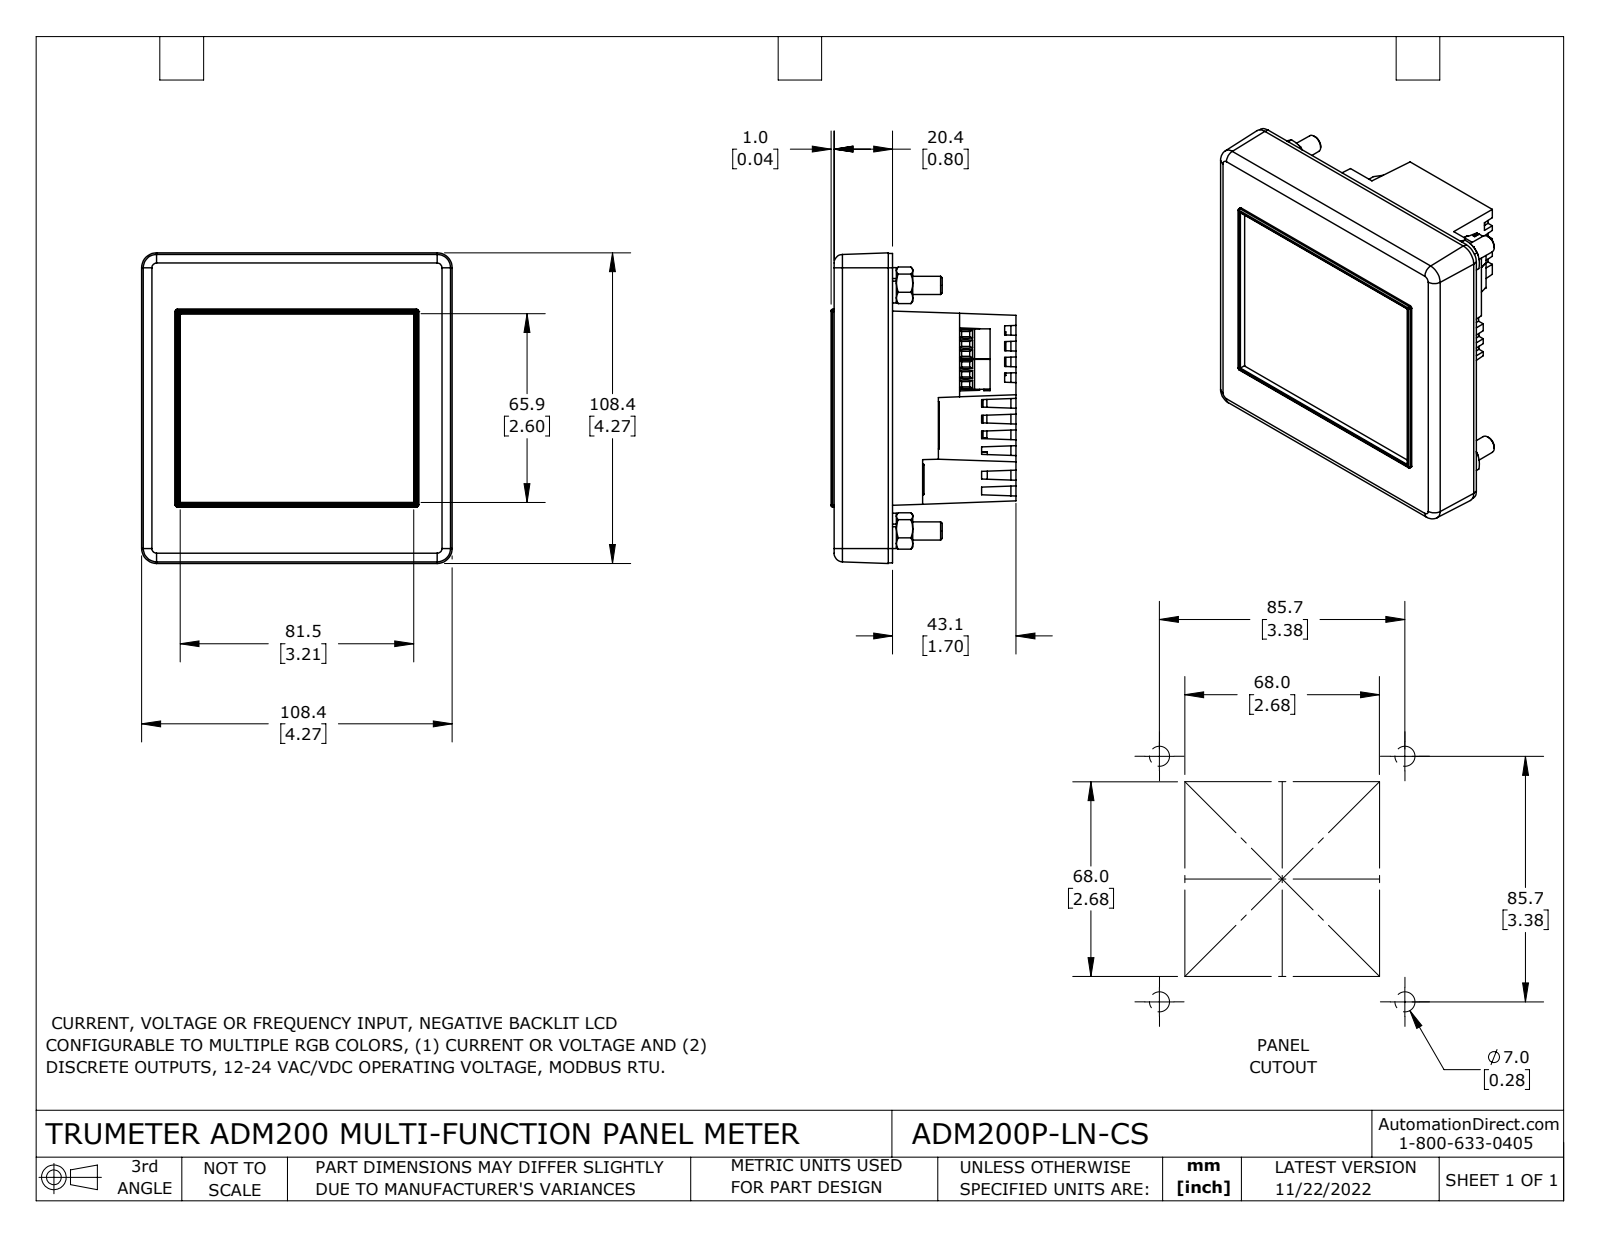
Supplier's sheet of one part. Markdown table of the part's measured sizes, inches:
| quantity | value |
| --- | --- |
| part name | ADM200P-LN-CS |
| STEP written by | SolidWorks 2021 (CONFIG_CONTROL_DESIGN) |
| units | inches |
| bodies | 23 solids, 2059 faces (1384 planar, 290 cylindrical, 385 other) |
| overall size | 4.269 × 4.269 × 2.541 |
| volume | 7.808 in³ |
| surface area | 190.8 in² |
| round holes (diameter × count) | 0.071 × 9, 0.114 × 6, 0.118 × 5, 0.213 × 4, 0.25 × 4, 0.26 × 4, 0.295 × 4, 0.154 × 2 |
| round bosses / shafts (diameter × count) | 0.039 × 5, 0.487 × 4, 0.438 × 4, 0.024 × 4, 0.079 × 2 |
| partial cylindrical surfaces (radius × count) | 0.006 × 32, 0.02 × 30, 0.039 × 7, 0.016 × 4, 0.03 × 4, 0.118 × 4, 0.197 × 4, 0.004 × 2 |
| main face-to-face distances | 0.031, 0.635, 0.11, 0.073, 0.059, 0.079, 0.694, 3.395, 3.468, 0.047 |
| hole center spacings | 0.709, 3.228, 0.136, 0.293, 0.986, 1.417, 2.126, 2.399 |
